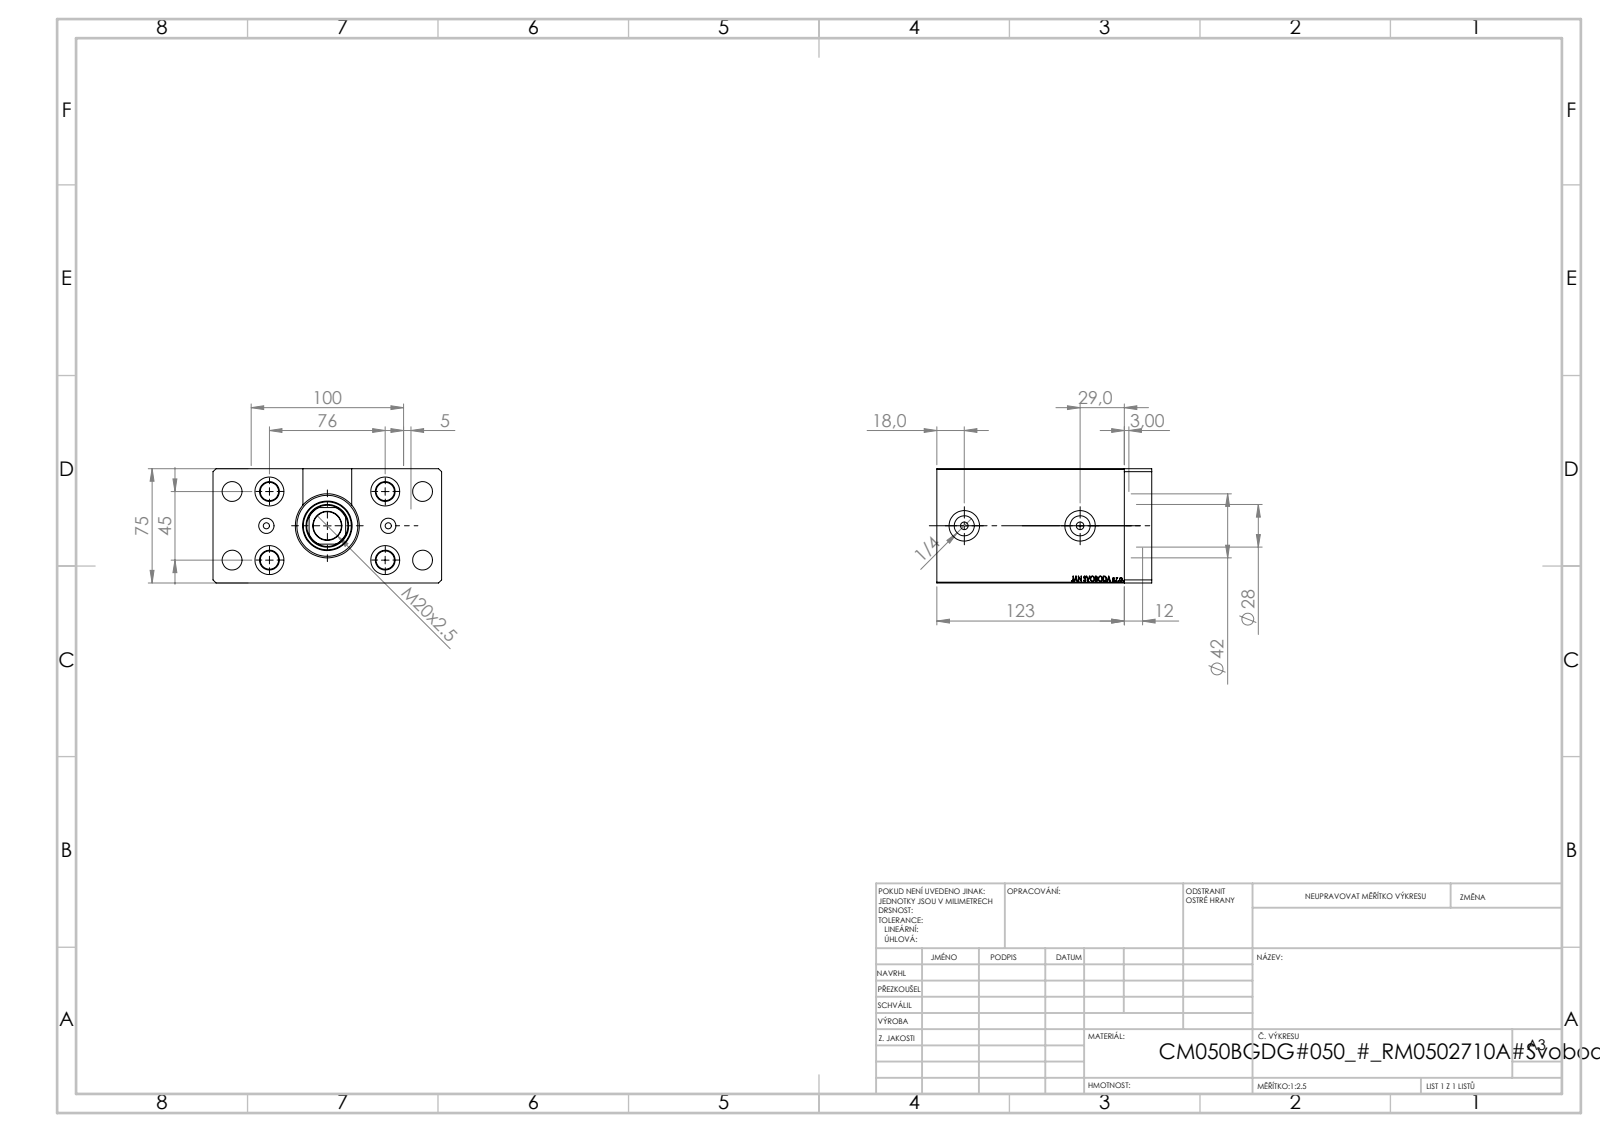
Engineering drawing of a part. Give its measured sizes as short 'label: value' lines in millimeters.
name: V450CM_B_Body; Zatka_OIL_PORT; FLANGE; V450CM_VC_B (+1 more)
written by: SolidWorks 2019 (CONFIG_CONTROL_DESIGN)
unit: mm
bodies: 6 solids, 991 faces (455 planar, 106 cylindrical, 430 other)
size: 150 × 141 × 75
volume: 977 026 mm³; area: 147 553 mm²
holes: 8× ⌀13, 4× ⌀12, 4× ⌀19, 2× ⌀4, 2× ⌀5, 2× ⌀10, 2× ⌀13.16, 2× ⌀20, 1× ⌀18.5, 1× ⌀28, 1× ⌀31.5, 1× ⌀32.5
bosses: 2× ⌀18
rounds: 1× R13.5
face distances: 75, 100, 18, 141, 123, 14, 109, 127, 125, 25
hole spacings: 22.59, 24.5, 31.82, 44.16, 45, 51.24, 66.43, 81.18
